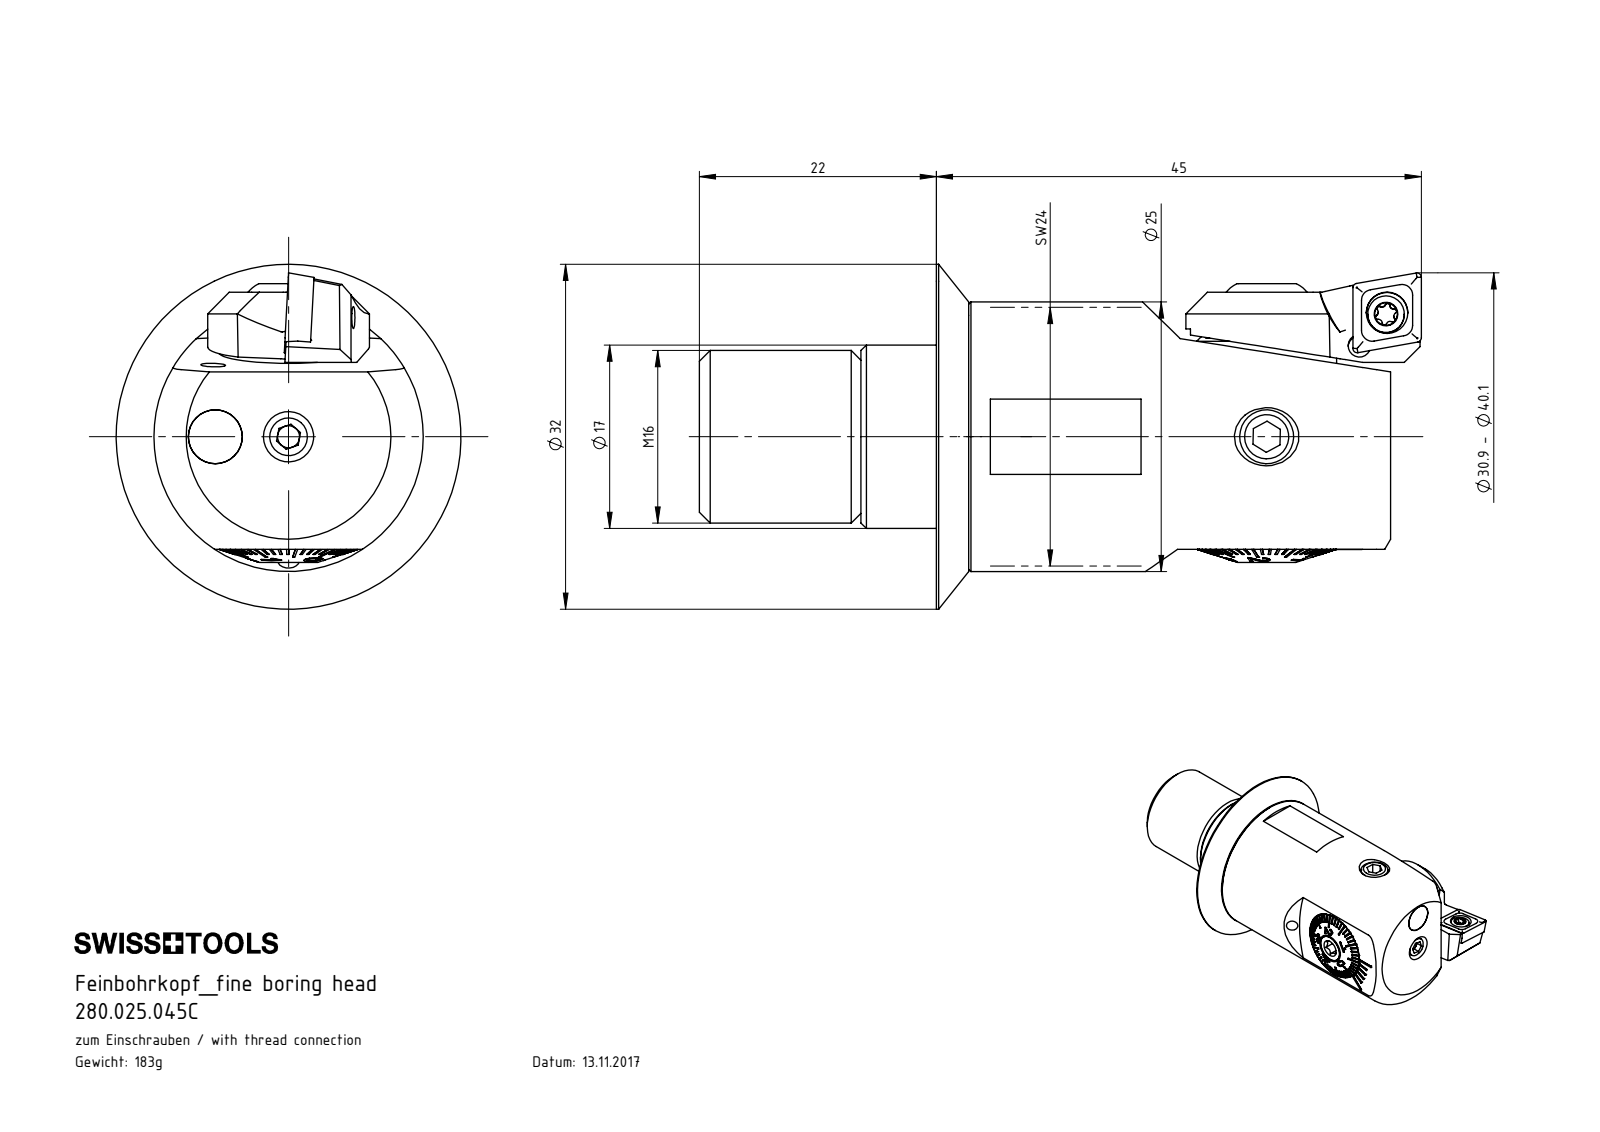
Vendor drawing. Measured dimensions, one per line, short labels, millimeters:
name: F25-BG1.012.013; F25-BG1.009.006_A; F25-BG2.008.009_A; 280.025.045C (+8 more)
written by: SolidWorks 2017 (CONFIG_CONTROL_DESIGN)
unit: mm
bodies: 20 solids, 834 faces (366 planar, 154 cylindrical, 314 other)
size: 67 × 32 × 32
volume: 23 344 mm³; area: 14 939 mm²
holes: 5× ⌀2, 2× ⌀2.05, 2× ⌀4.2, 1× ⌀2.1, 1× ⌀2.4, 1× ⌀2.7, 1× ⌀2.8, 1× ⌀3, 1× ⌀3.3, 1× ⌀3.85, 1× ⌀5, 1× ⌀5.5
bosses: 2× ⌀5, 2× ⌀4.95, 2× ⌀2.5, 1× ⌀32, 1× ⌀25, 1× ⌀16, 1× ⌀12.98, 1× ⌀12.85
rounds: 6× R0.21, 5× R0.36, 4× R0.5, 2× R1.32, 1× R0.2, 1× R0.36, 1× R1.05, 1× R1.25
face distances: 3, 42.15, 39.15, 8, 1.5, 15, 19.95, 3.1, 15.7, 0.8
hole spacings: 3.84, 3.99, 4.48, 6.8, 9.46, 16.65
